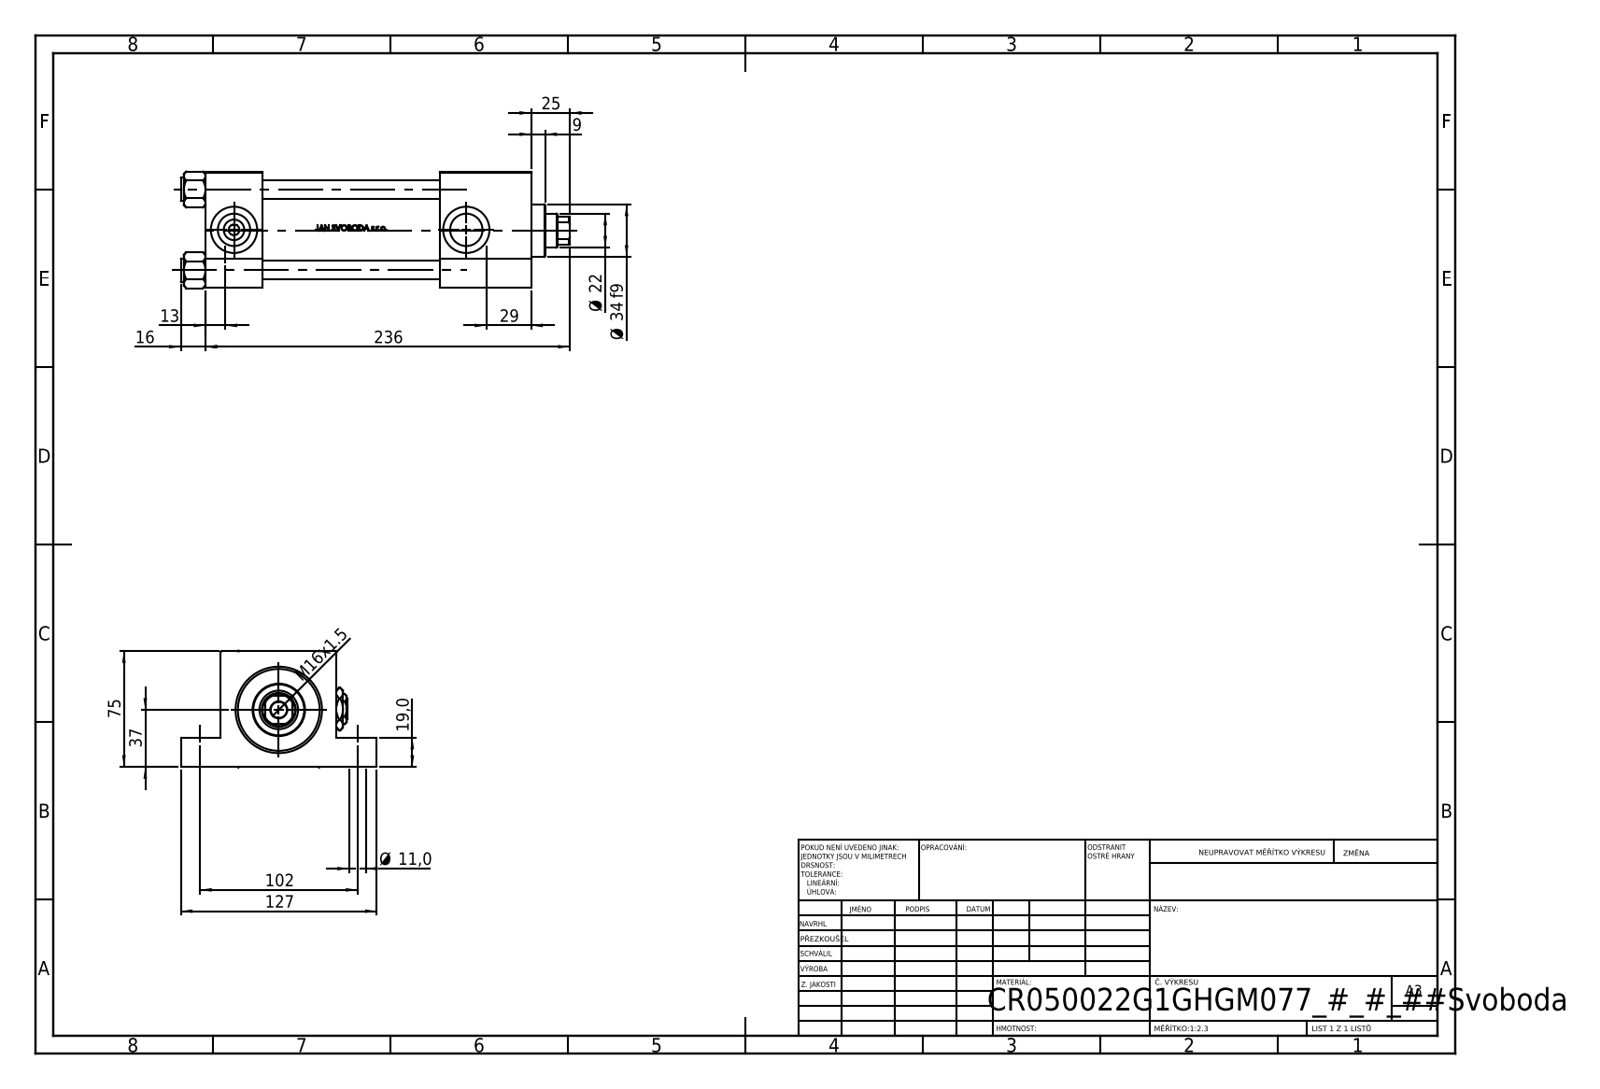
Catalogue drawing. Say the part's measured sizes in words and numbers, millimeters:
The part is named "V215CR_VCP_G; V215_VC_A; V215CR_G_Body; NUT_M5_G (+2 more)". Its 3-D file was written by "SolidWorks 2019 (CONFIG_CONTROL_DESIGN)". It is 12 solids with 1134 faces: 454 planar, 128 cylindrical and 552 other. Overall it measures 252 by 127 by 75.54 millimeters. Its volume is 828 329 cubic millimeters and its surface area 192 820 square millimeters. Round holes: 4 of diameter 11, 4 of diameter 12, 2 of diameter 7, 2 of diameter 20.96, 2 of diameter 30, 1 of diameter 10.5, 1 of diameter 22, 1 of diameter 25, 1 of diameter 41, 1 of diameter 50, 1 of diameter 53. Round bosses or shafts: 4 of diameter 15, 1 of diameter 56, 1 of diameter 34. Partial cylindrical surfaces (rounded edges, fillets, slot ends): 1 of radius 10.5. The main face-to-face distances are 75, 37, 211, 174, 19, 56, 152, 115, 59, 26. The hole center spacings are 52.3, 36.63, 37.34, 73.96, 102, 169, 197.4, 150.5.
